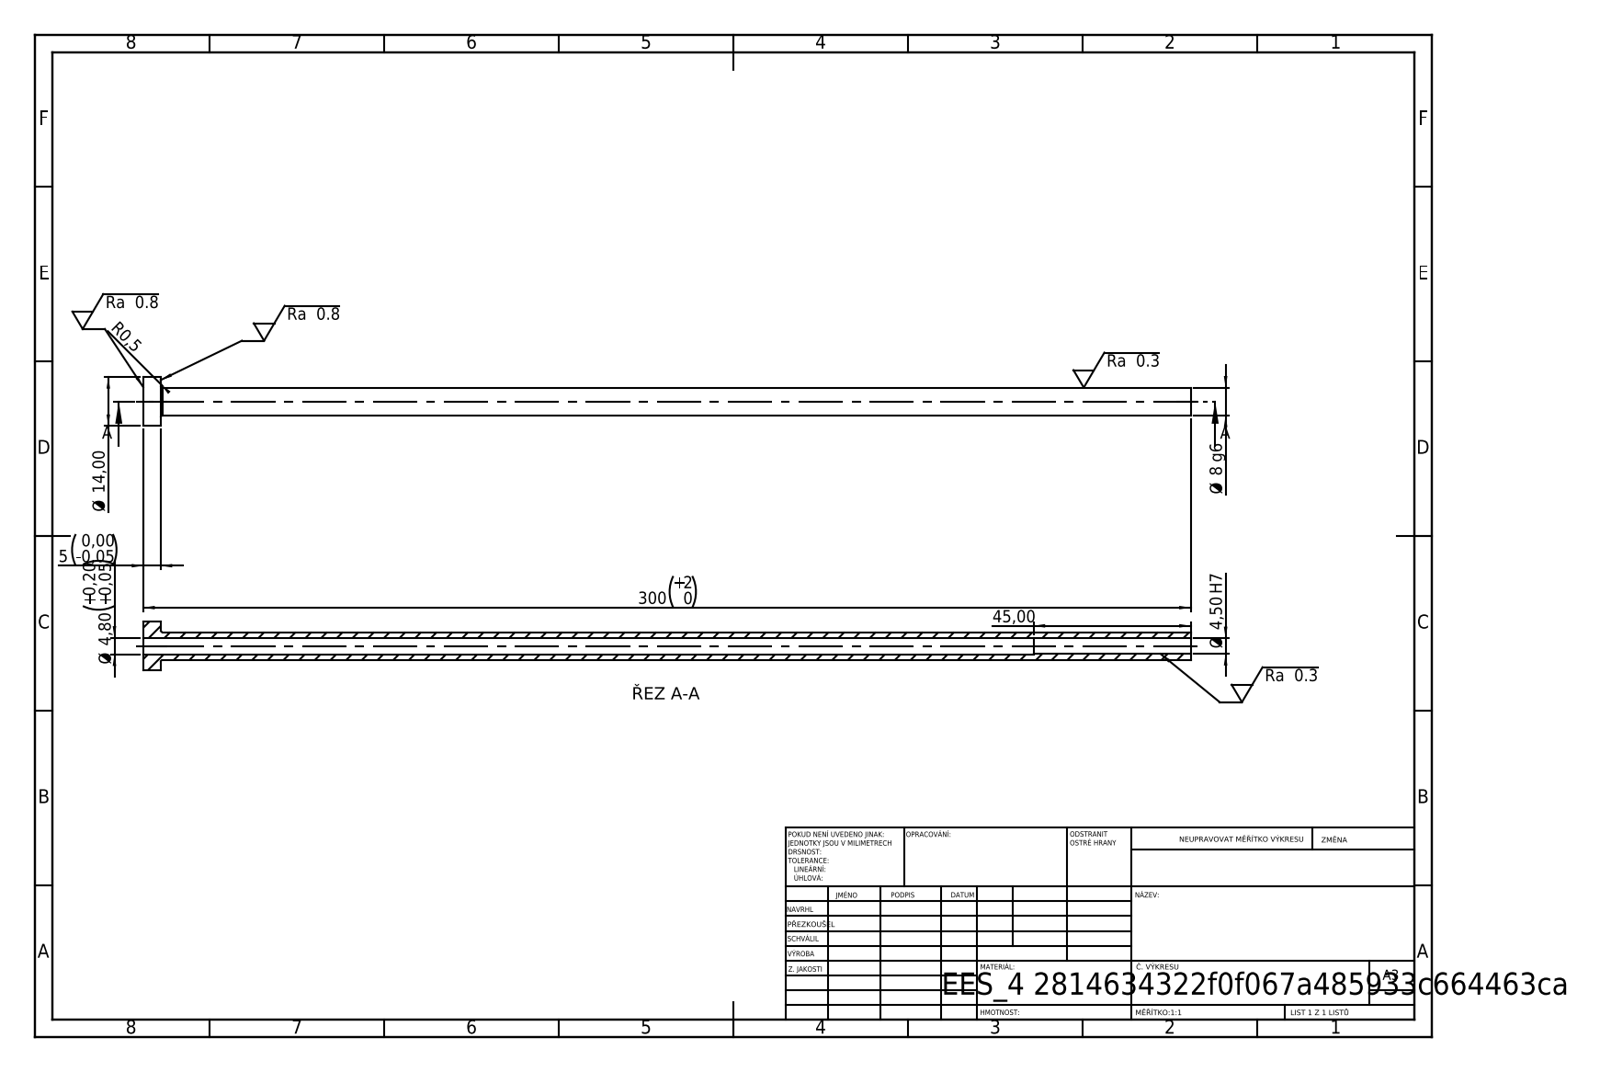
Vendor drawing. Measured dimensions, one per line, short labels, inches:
written by: SolidWorks 2019 (CONFIG_CONTROL_DESIGN)
unit: in
bodies: 1 solid, 14 faces (4 planar, 8 cylindrical, 2 other)
size: 11.811 × 0.551 × 0.551
volume: 0.627 in³; area: 19.2 in²
holes: 1× ⌀0.177, 1× ⌀0.189
bosses: 1× ⌀0.551, 1× ⌀0.315
face distances: 0.197, 11.811, 11.614, 10.039, 9.843, 1.772
